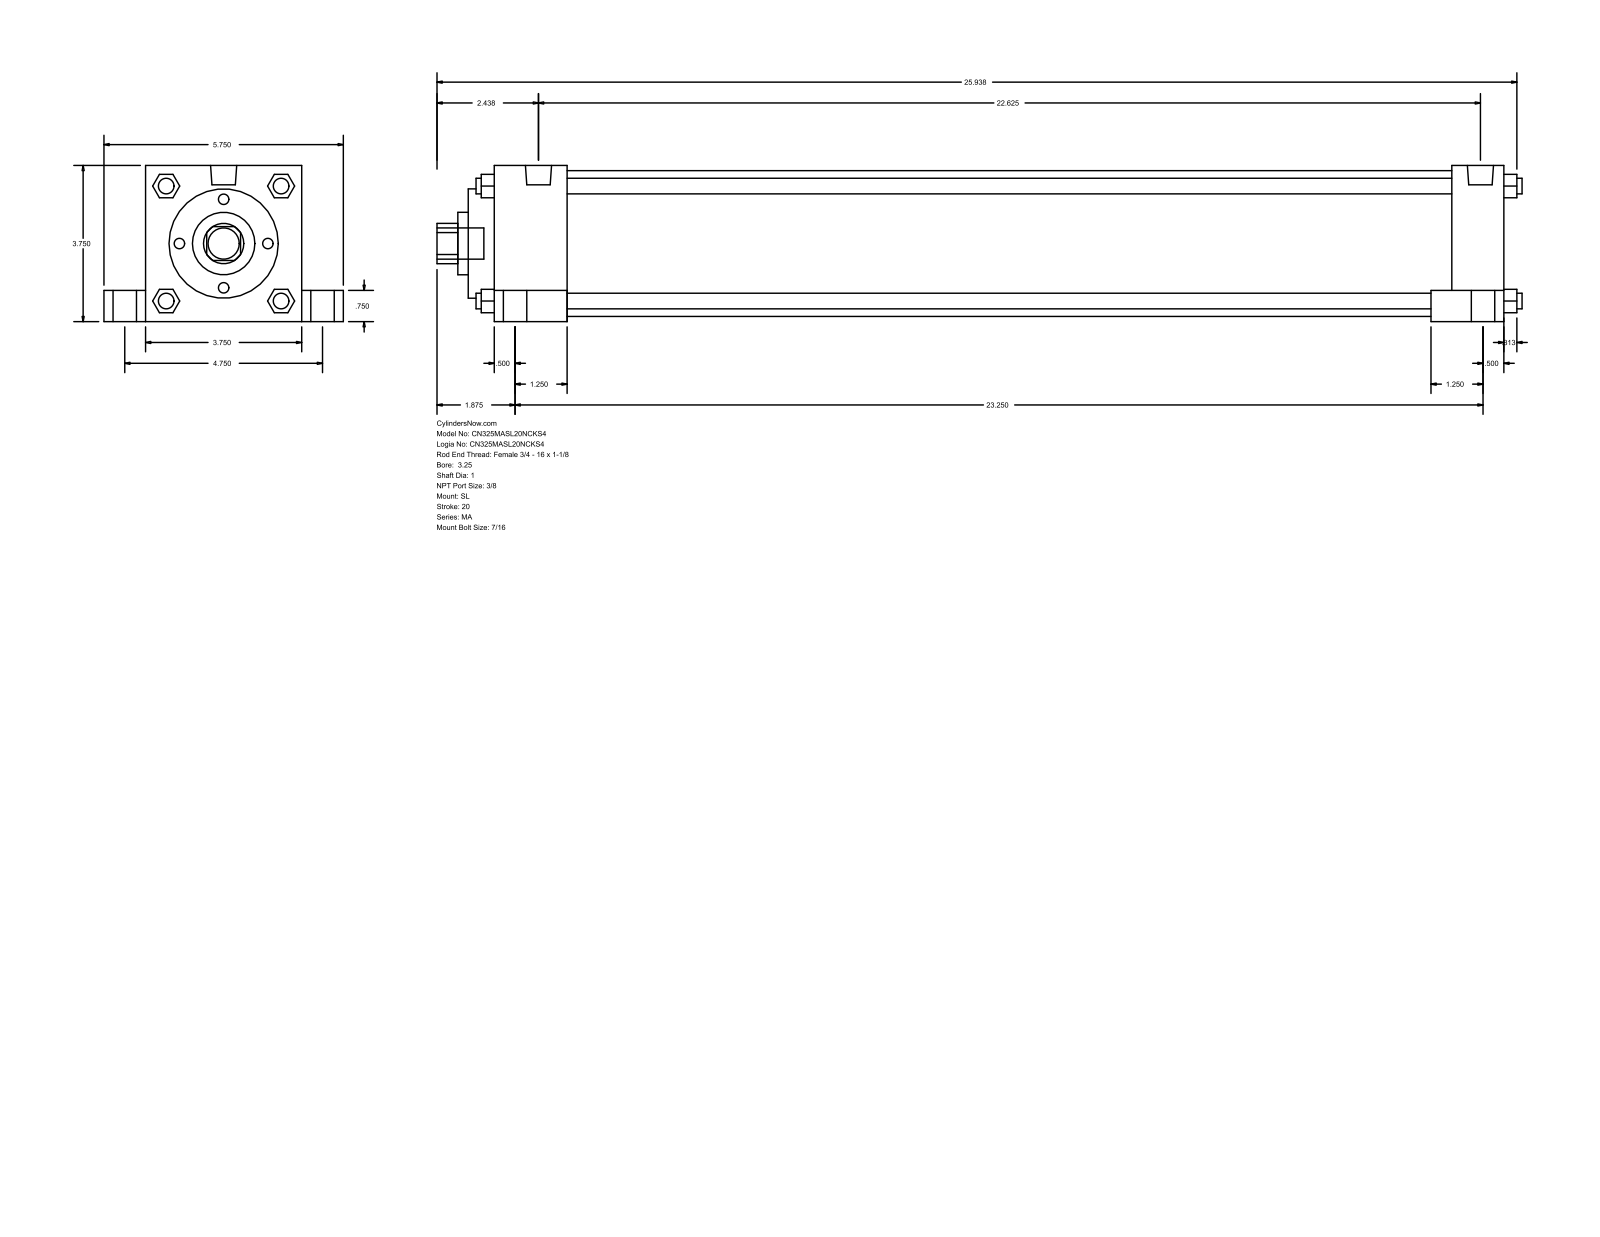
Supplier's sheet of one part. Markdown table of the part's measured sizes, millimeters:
| quantity | value |
| --- | --- |
| part name | MA_SL__0325_1 |
| STEP written by | GSSL Pune (CONFIG_CONTROL_DESIGN) |
| units | millimeters |
| bodies | 0 solids, 150 faces (113 planar, 37 cylindrical, 0 other) |
| overall size | 661.99 × 146.05 × 95.25 |
| round holes (diameter × count) | 25.4 × 1, 38.1 × 1, 66.67 × 1, 88.9 × 1 |
| round bosses / shafts (diameter × count) | 20.64 × 4, 14.29 × 4, 11.11 × 4, 9.53 × 4, 15.93 × 2, 19.05 × 1 |
| partial cylindrical surfaces (radius × count) | 12.29 × 1 |
| main face-to-face distances | 95.24, 615.96, 15.87, 25.41, 120.65, 19.05, 584.2, 31.76, 44.46, 539.74 |
